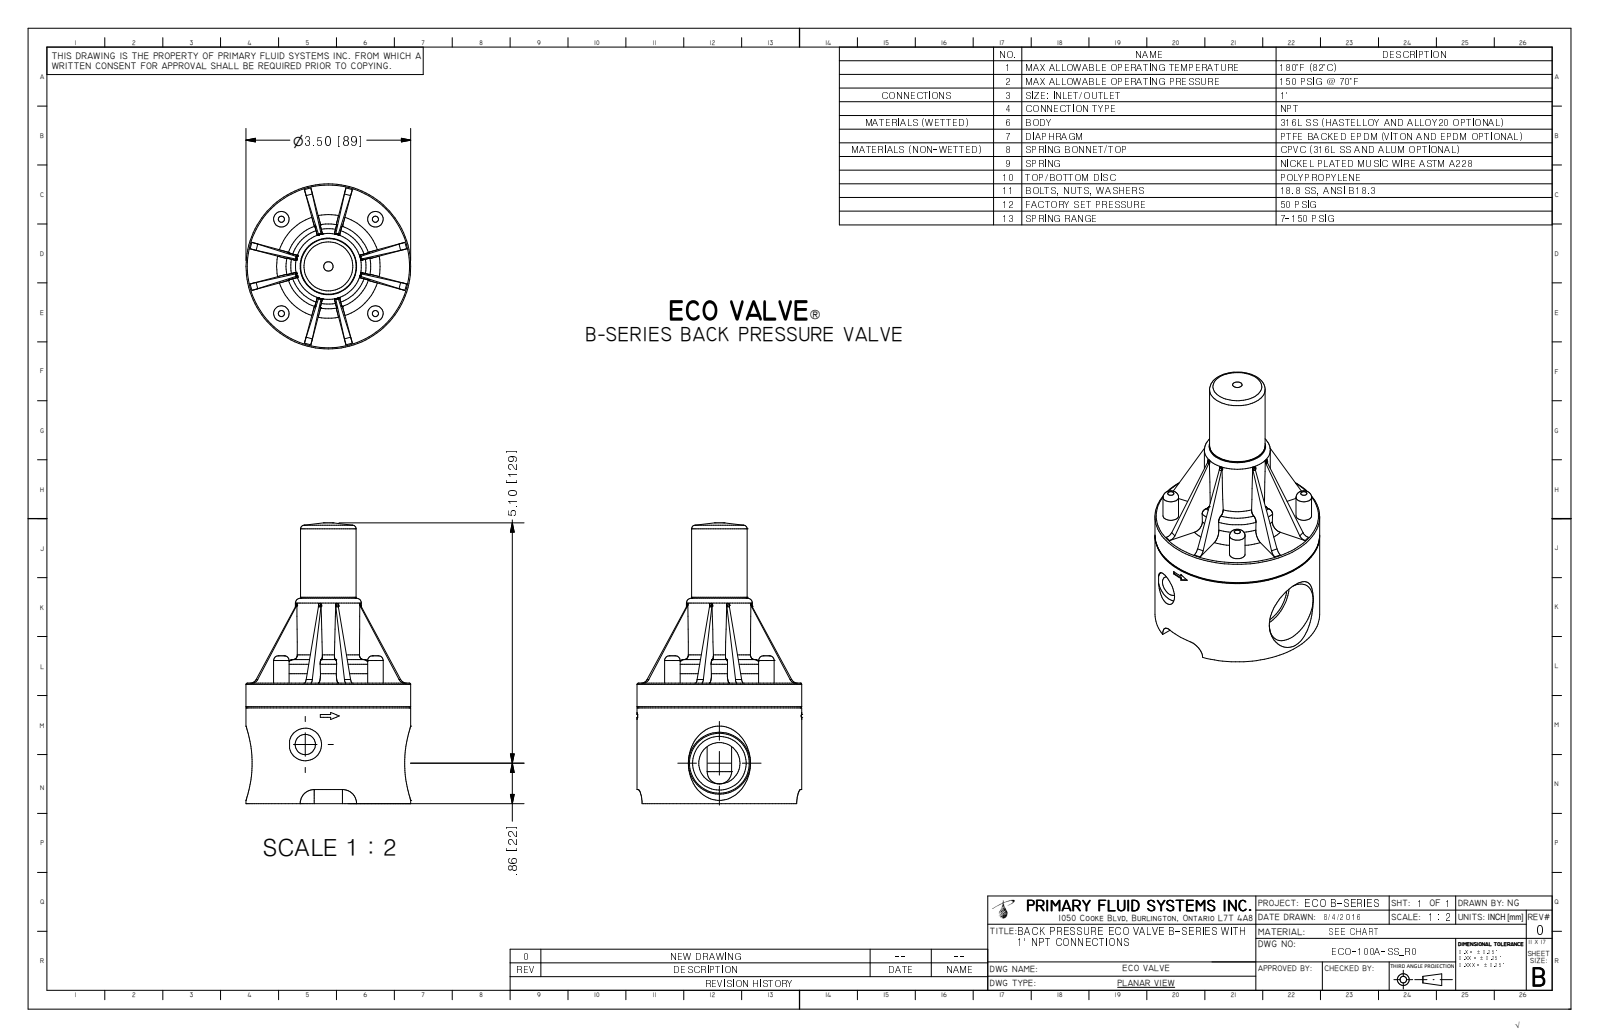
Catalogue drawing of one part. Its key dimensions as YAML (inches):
part_name: "ECO-100A-SS_R0"
step_written_by: "Autodesk Inventor 2009 (AUTOMOTIVE_DESIGN)"
units: inches
bodies: {solids: 1, faces: 179, planar: 72, cylindrical: 45, other: 62}
overall_size: [5.955, 3.5, 3.5]
volume: 27.21
surface_area: 88.64
round_holes:
  - {diameter: 0.23, count: 2}
  - {diameter: 0.256, count: 2}
  - {diameter: 0.257, count: 2}
  - {diameter: 0.4, count: 2}
  - {diameter: 0.431, count: 1}
  - {diameter: 0.691, count: 1}
round_bosses_or_shafts:
  - {diameter: 0.33, count: 4}
  - {diameter: 3.5, count: 1}
  - {diameter: 1.8, count: 1}
  - {diameter: 1.4, count: 1}
  - {diameter: 1.18, count: 1}
partial_cylinders:
  - {radius: 0.15, count: 8}
  - {radius: 0.3, count: 4}
  - {radius: 1.73, count: 1}
face_to_face_distances: [2.555, 1.84, 0.3, 2.255, 1.73, 0.27, 2.03, 0.525, 0.15, 1.88]
hole_center_spacings: [2.828]
